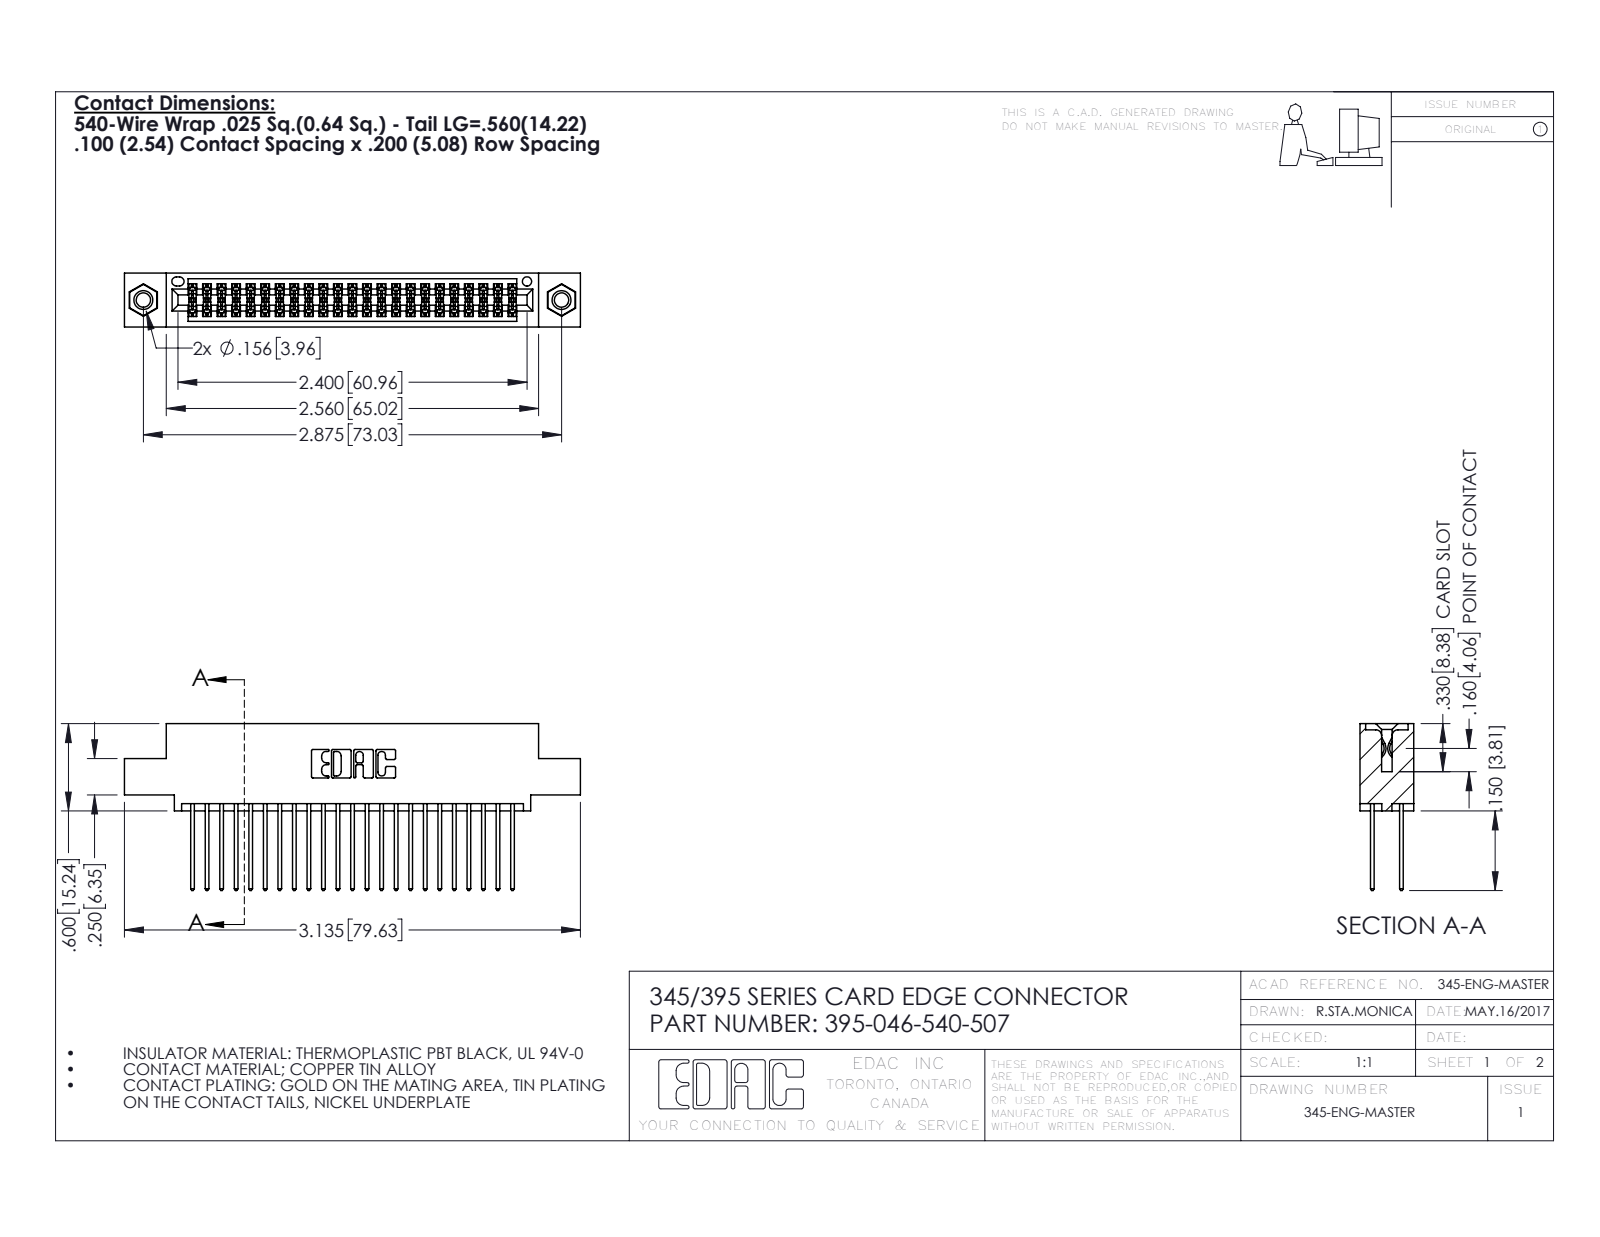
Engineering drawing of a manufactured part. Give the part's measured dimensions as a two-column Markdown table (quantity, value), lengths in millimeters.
| quantity | value |
| --- | --- |
| part name | 395-046-540-507; 345-250-001_345-250-005-103; 345 Part_0.110 Offset - 0.156 Dia-TI; 345-292-001_345-293-140 |
| STEP written by | SolidWorks 2016 (CONFIG_CONTROL_DESIGN) |
| units | millimeters |
| bodies | 49 solids, 2490 faces (1634 planar, 840 cylindrical, 16 other) |
| overall size | 79.6 × 29.1 × 9.4 |
| volume | 7 650 mm³ |
| surface area | 11 860 mm² |
| round holes (diameter × count) | 2.5 × 2, 3.2 × 2, 4 × 2, 1.6 × 1 |
| round bosses / shafts (diameter × count) | 3.9 × 2 |
| partial cylindrical surfaces (radius × count) | 0.2 × 69, 0.3 × 46, 0.3 × 22, 0.2 × 6, 0.8 × 6, 0.7 × 3, 0.4 × 2, 0.5 × 2 |
| main face-to-face distances | 1.8, 7.6, 5.1, 2.5, 6.9, 0.6, 9.4, 5.7, 4.4, 3.8 |
| hole center spacings | 6.9, 67.1, 73 |
